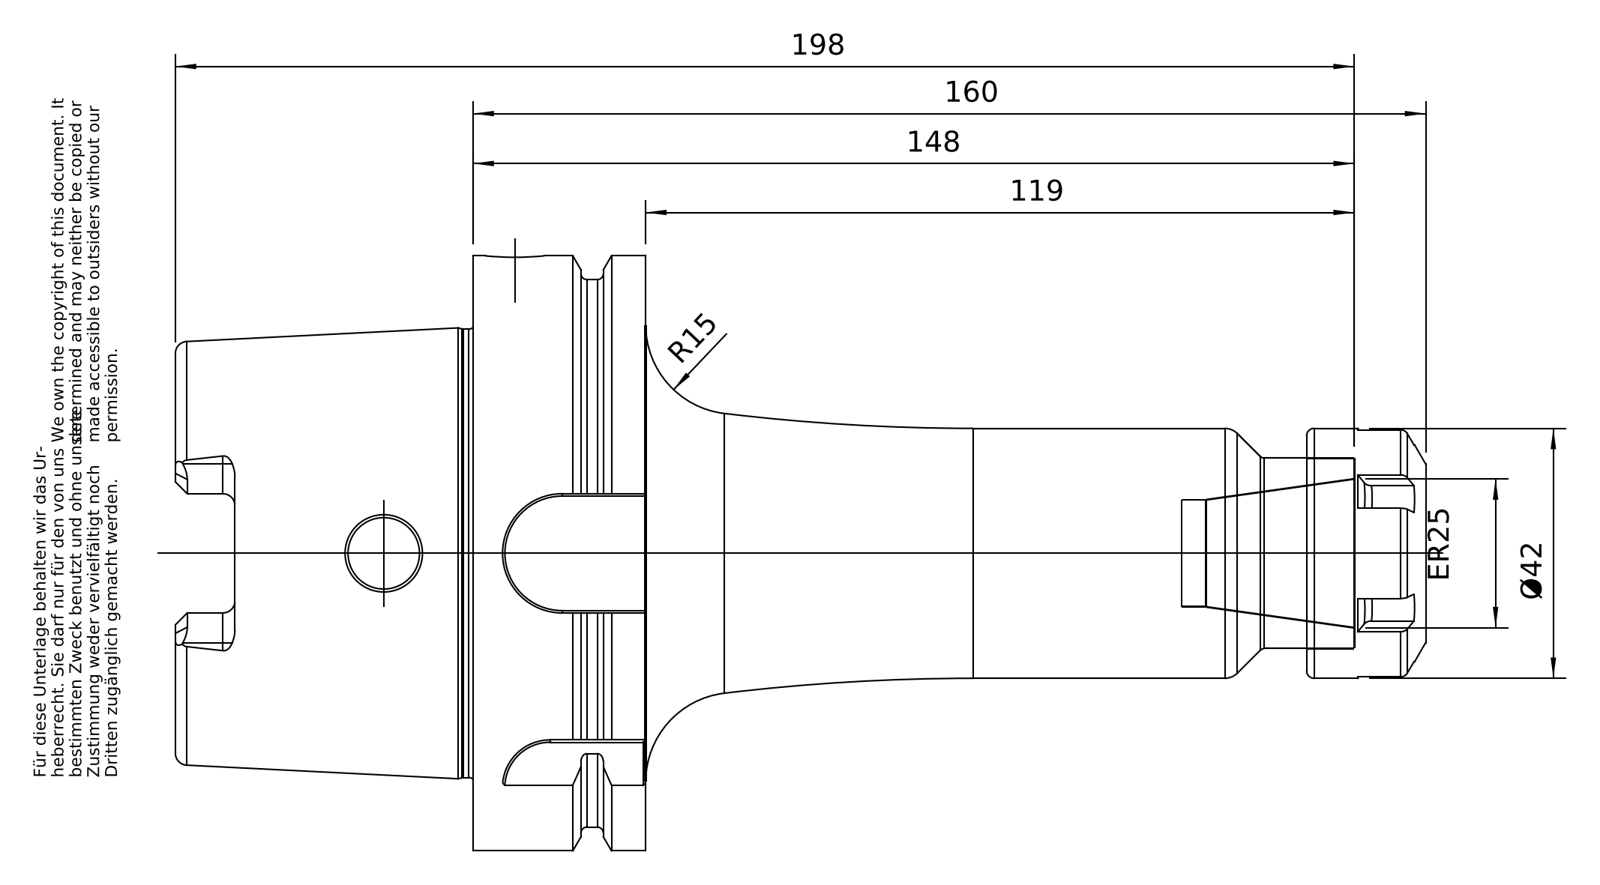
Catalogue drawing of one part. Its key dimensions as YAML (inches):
part_name: "A100-022-25; 83-912-25; A100-022-25_ASM"
step_written_by: "PRO/ENGINEER BY PARAMETRIC TECHNOLOGY CORPORATION, 2010430 (CONFIG_CONTROL_DESIGN)"
units: inches
bodies: {solids: 2, faces: 227, planar: 72, cylindrical: 54, other: 101}
overall_size: [8.268, 3.937, 3.937]
volume: 26.92
surface_area: 110.3
round_holes:
  - {diameter: 0.394, count: 1}
  - {diameter: 0.472, count: 1}
  - {diameter: 0.709, count: 1}
  - {diameter: 0.886, count: 1}
  - {diameter: 0.945, count: 1}
  - {diameter: 0.957, count: 1}
  - {diameter: 0.965, count: 1}
  - {diameter: 2.087, count: 1}
  - {diameter: 2.48, count: 1}
round_bosses_or_shafts:
  - {diameter: 3.937, count: 1}
  - {diameter: 3.622, count: 1}
  - {diameter: 2.967, count: 1}
  - {diameter: 1.654, count: 1}
  - {diameter: 1.26, count: 1}
partial_cylinders:
  - {radius: 0.079, count: 6}
  - {radius: 0.197, count: 4}
  - {radius: 0.315, count: 1}
  - {radius: 0.394, count: 1}
  - {radius: 0.434, count: 1}
face_to_face_distances: [1.142, 0.492, 0.65, 5.512, 5.02, 4.37, 1.969, 2.461, 3.11, 7.48]
